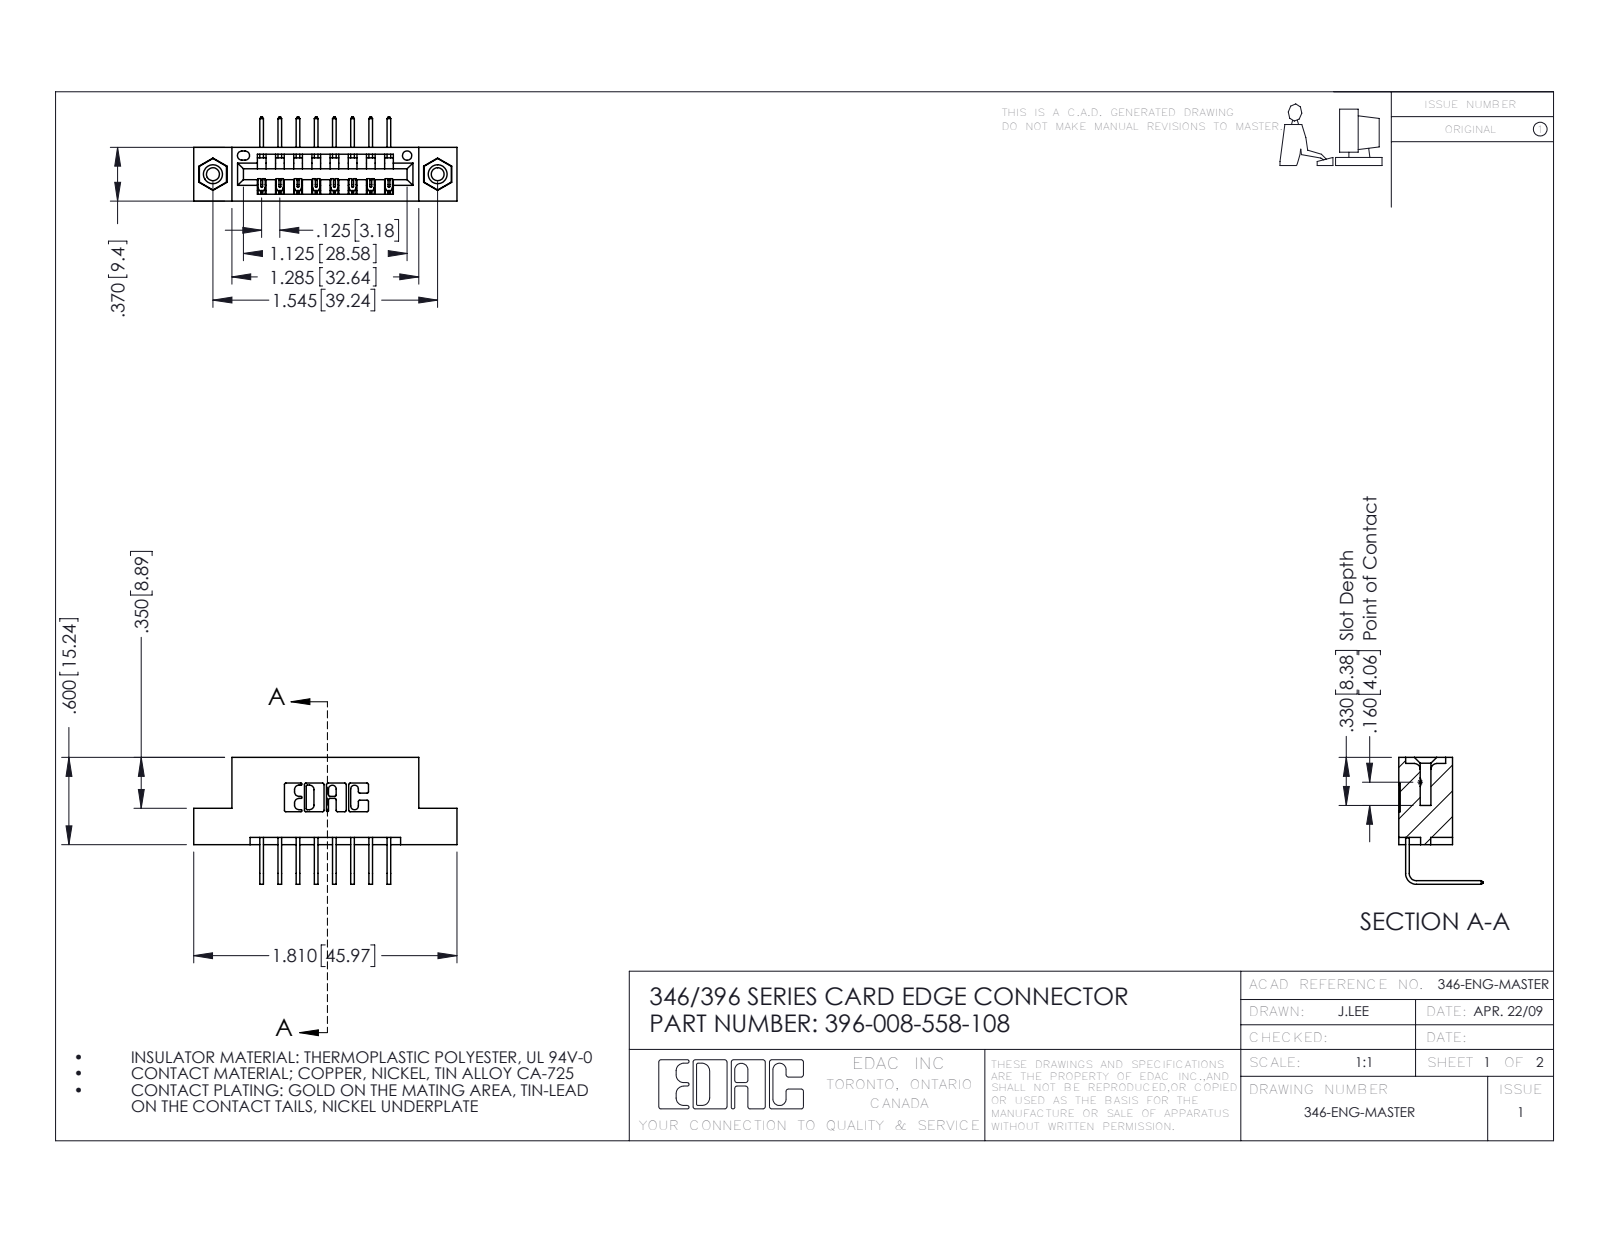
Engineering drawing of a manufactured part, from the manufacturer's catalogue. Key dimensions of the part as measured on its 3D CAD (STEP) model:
Part name (STEP PRODUCT): 345-250-001_345-250-003-102; 396-008-558-108; 345-292-001_558 Tail - 2; 346 Part_Flush Mounting Lugs - 0.156 Dia-TI
STEP written by: SolidWorks 2016 (CONFIG_CONTROL_DESIGN)
Units: inches
Bodies: 11 solids, 662 faces (444 planar, 202 cylindrical, 16 other)
Overall size (bounding box): 1.81 × 0.873 × 0.58
Volume: 0.255 in³ · Surface area: 7.822 in²
Round holes (diameter × count): ⌀0.089 ×2, ⌀0.125 ×2, ⌀0.156 ×2, ⌀0.064 ×1
Round bosses / shafts (diameter × count): ⌀0.155 ×2
Partial cylindrical surfaces — rounded edges, fillets, slot ends (radius × count): R0.01 ×22, R0.006 ×16, R0.007 ×6, R0.031 ×6, R0.026 ×3, R0.031 ×2, R0.04 ×2, R0.014 ×1
Main face-to-face distances: 0.25, 0.322, 0.37, 0.048, 0.298, 0.025, 0.5, 0.148, 0.222, 0.1
Hole centre spacings: 0.246, 1.341, 1.545
